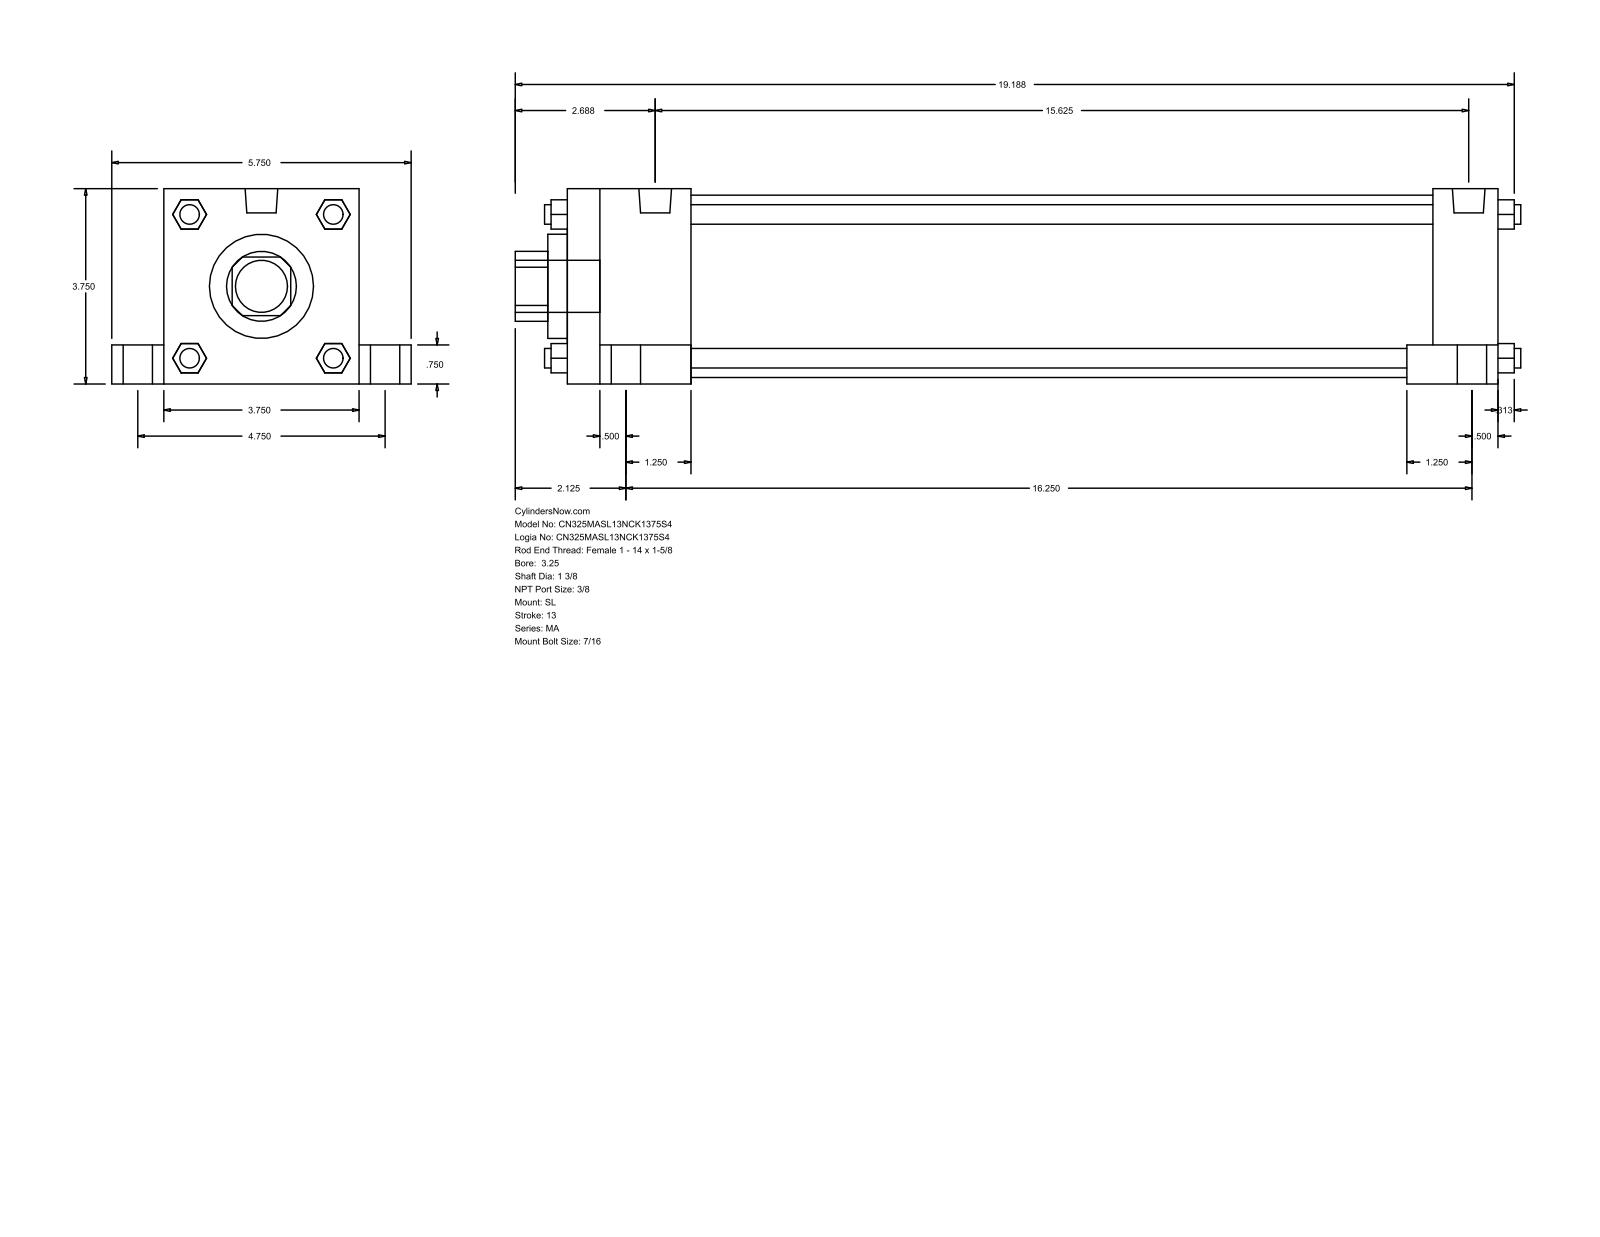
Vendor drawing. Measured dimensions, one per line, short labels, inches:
name: MA_SL__0325_1.375
written by: GSSL Pune (CONFIG_CONTROL_DESIGN)
unit: in
bodies: 0 solids, 148 faces (112 planar, 36 cylindrical, 0 other)
size: 19.313 × 5.75 × 3.75
holes: 1× ⌀1.375, 1× ⌀2, 1× ⌀3.5
bosses: 4× ⌀0.813, 4× ⌀0.563, 4× ⌀0.437, 4× ⌀0.375, 2× ⌀0.627, 1× ⌀1
rounds: 1× R0.672
face distances: 3.75, 17.875, 1, 4.75, 16.625, 1.25, 2.375, 14.25, 15.5, 0.75
